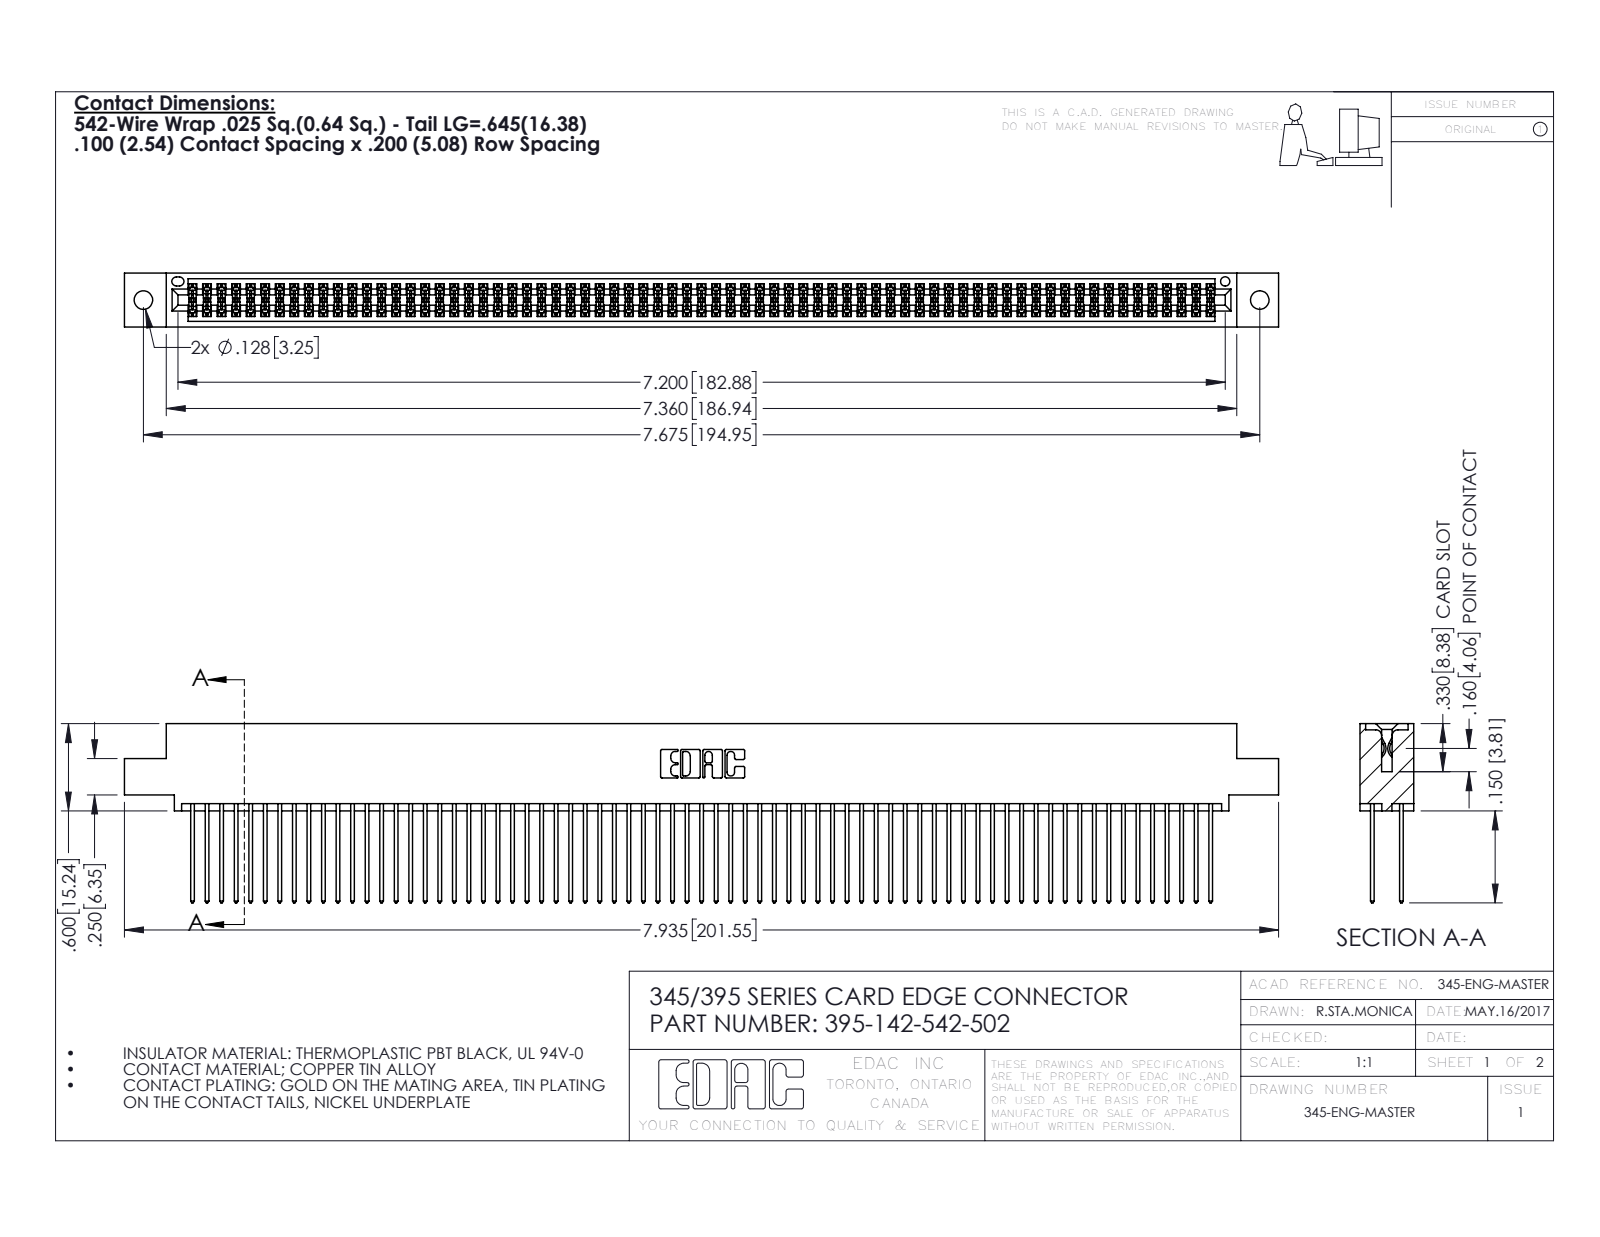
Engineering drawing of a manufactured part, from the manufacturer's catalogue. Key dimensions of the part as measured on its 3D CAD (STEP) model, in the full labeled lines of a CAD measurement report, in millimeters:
Part name (STEP PRODUCT): 395-142-542-502; 345-292-001_345-293-142; 345 Part_0.110 Offset - 0.128 Dia
STEP written by: SolidWorks 2016 (CONFIG_CONTROL_DESIGN)
Units: millimetres
Bodies: 143 solids, 7230 faces (4770 planar, 2460 cylindrical, 0 other)
Overall size (bounding box): 201.5 × 31.3 × 9.4
Volume: 20 400 mm³ · Surface area: 33 630 mm²
Round holes (diameter × count): ⌀3.3 ×2, ⌀1.6 ×1
Partial cylindrical surfaces — rounded edges, fillets, slot ends (radius × count): R0.2 ×213, R0.3 ×142, R0.3 ×22, R0.2 ×6, R0.8 ×6, R0.7 ×3, R0.4 ×2, R0.5 ×2
Main face-to-face distances: 1.8, 7.6, 5.1, 2.5, 6.9, 0.6, 5.7, 9.4, 4.4, 3.8
Hole centre spacings: 6.9, 189, 194.9
